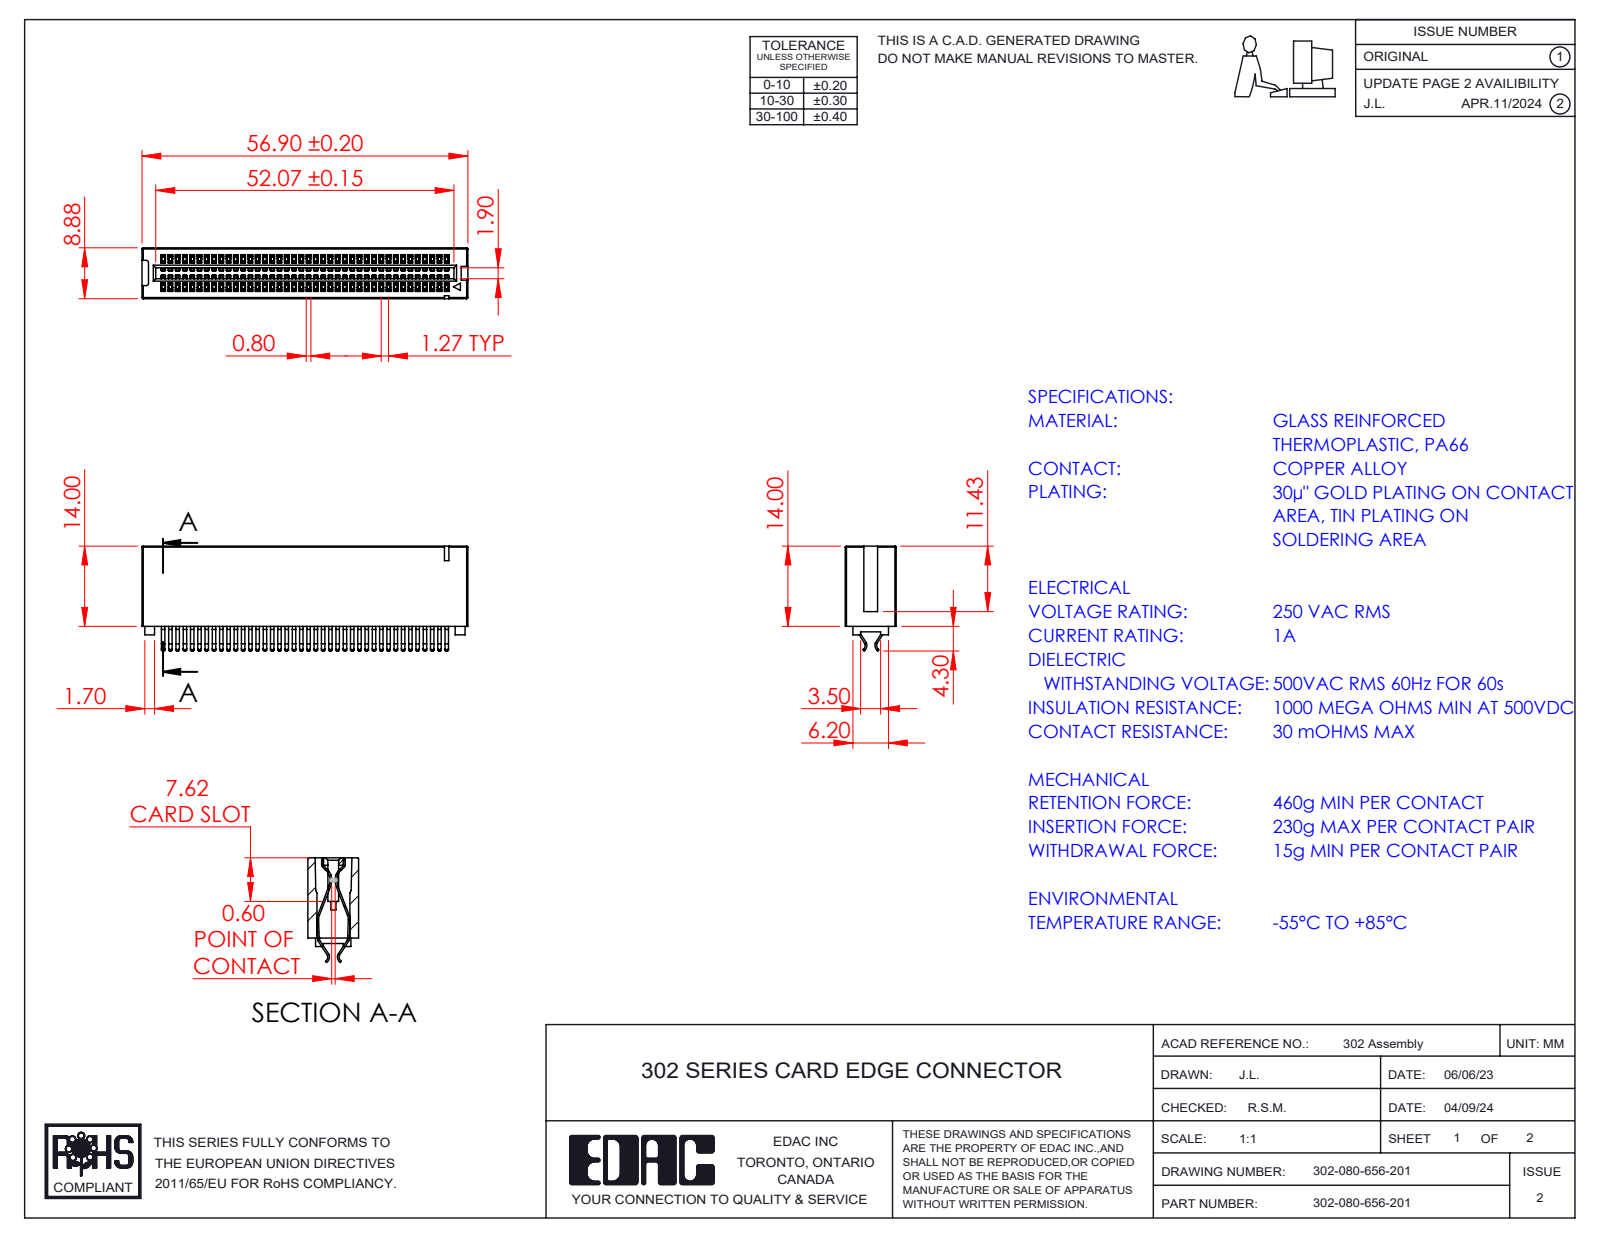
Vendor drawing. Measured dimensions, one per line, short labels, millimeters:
name: Contact_302-290-X56; HSG_Vertical HSG; 302-080-656-201
written by: SolidWorks 2023 (CONFIG_CONTROL_DESIGN)
unit: mm
bodies: 81 solids, 3866 faces (2569 planar, 1293 cylindrical, 4 other)
size: 56.9 × 18.3 × 8.88
volume: 4 408 mm³; area: 12 311 mm²
rounds: 248× R0.2, 2× R0.11, 2× R0.4, 2× R0.41, 2× R0.93, 2× R1.05, 2× R1.23, 2× R1.25
face distances: 1.27, 2.54, 3.81, 5.08, 7.62, 6.35, 8.88, 8.89, 10.16, 11.43
